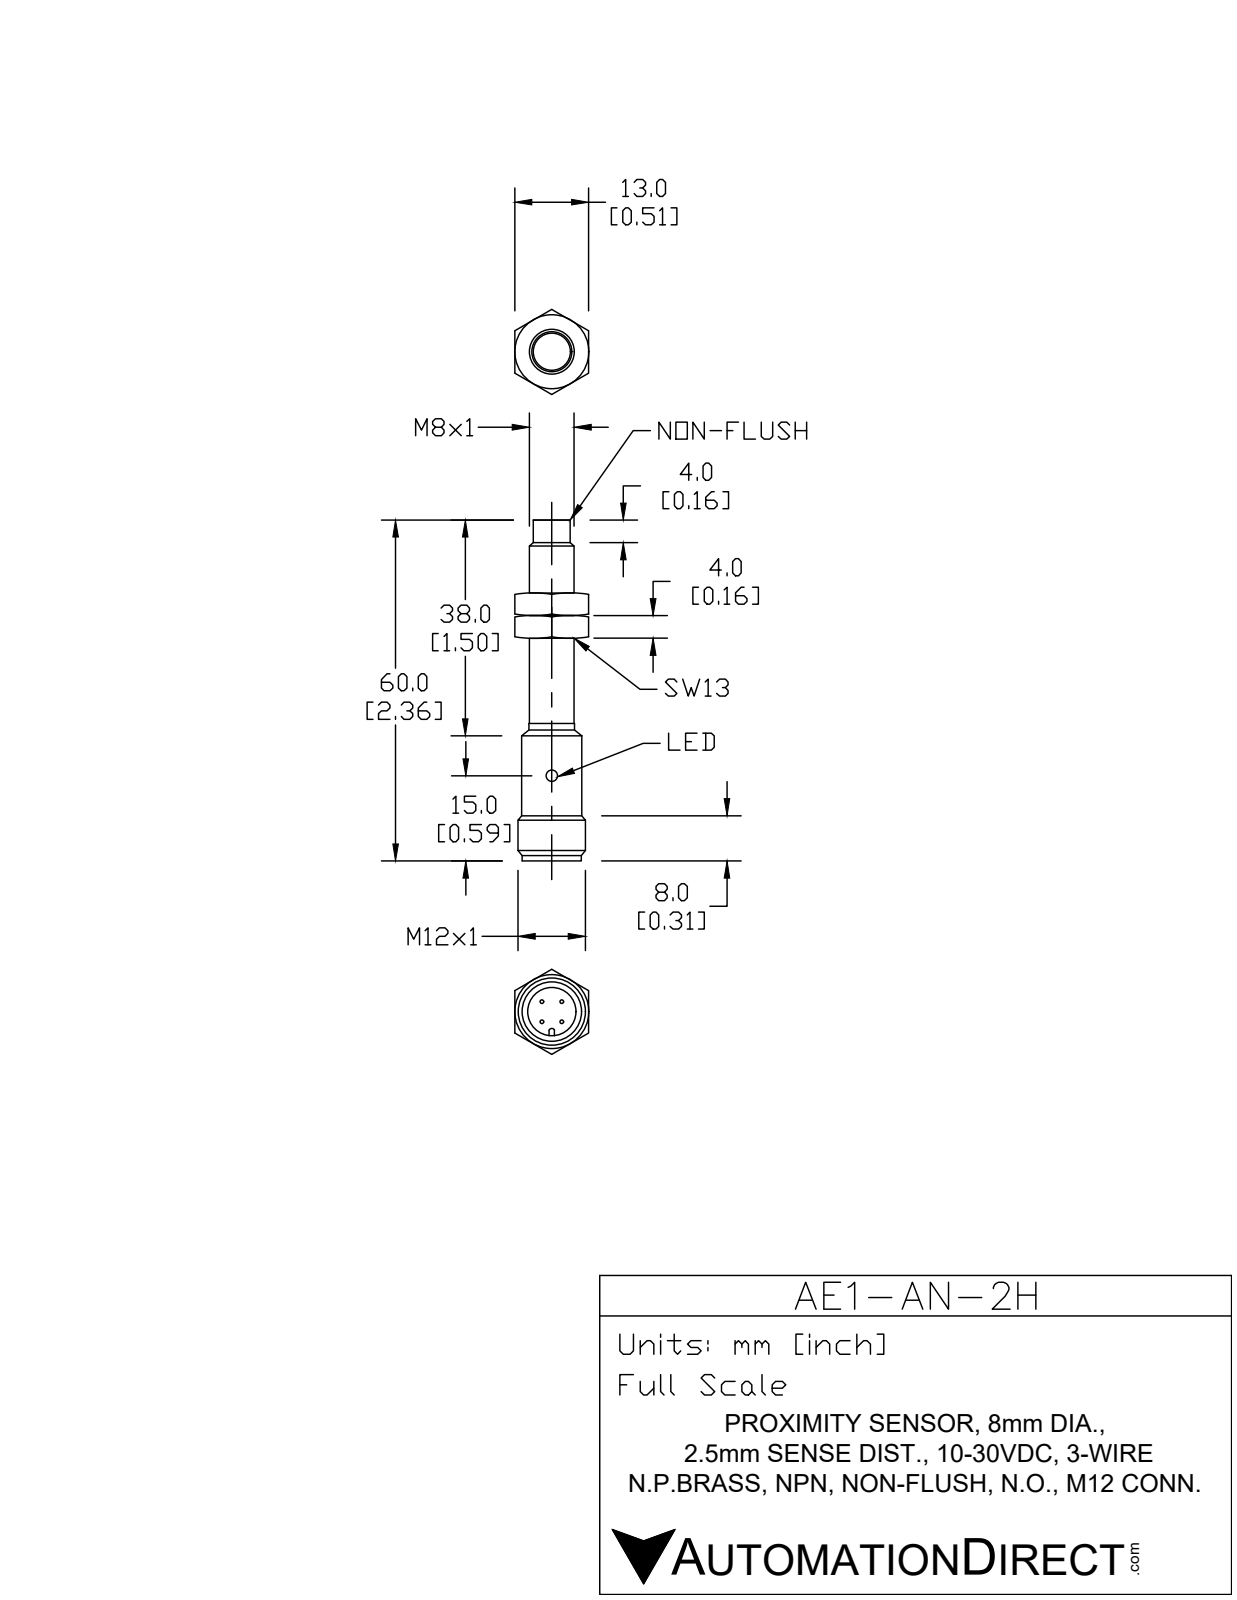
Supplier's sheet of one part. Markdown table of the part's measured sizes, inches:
| quantity | value |
| --- | --- |
| part name | AE1-AN-2H |
| STEP written by | SolidWorks 2017 (AUTOMOTIVE_DESIGN) |
| units | inches |
| bodies | 3 solids, 113 faces (22 planar, 59 cylindrical, 32 other) |
| overall size | 2.364 × 0.472 × 0.472 |
| volume | 0.156 in³ |
| surface area | 5.291 in² |
| round holes (diameter × count) | 0.079 × 4, 0.331 × 1, 0.386 × 1 |
| round bosses / shafts (diameter × count) | 0.039 × 4, 0.472 × 1, 0.413 × 1, 0.382 × 1, 0.378 × 1, 0.315 × 1, 0.256 × 1, 0.244 × 1 |
| partial cylindrical surfaces (radius × count) | 0.051 × 4, 0.02 × 1, 0.024 × 1, 0.051 × 1, 0.134 × 1 |
| main face-to-face distances | 0.446, 1.323, 1.769, 0.35, 0.157, 1.48, 1.927, 0.039, 2.013, 1.856 |
